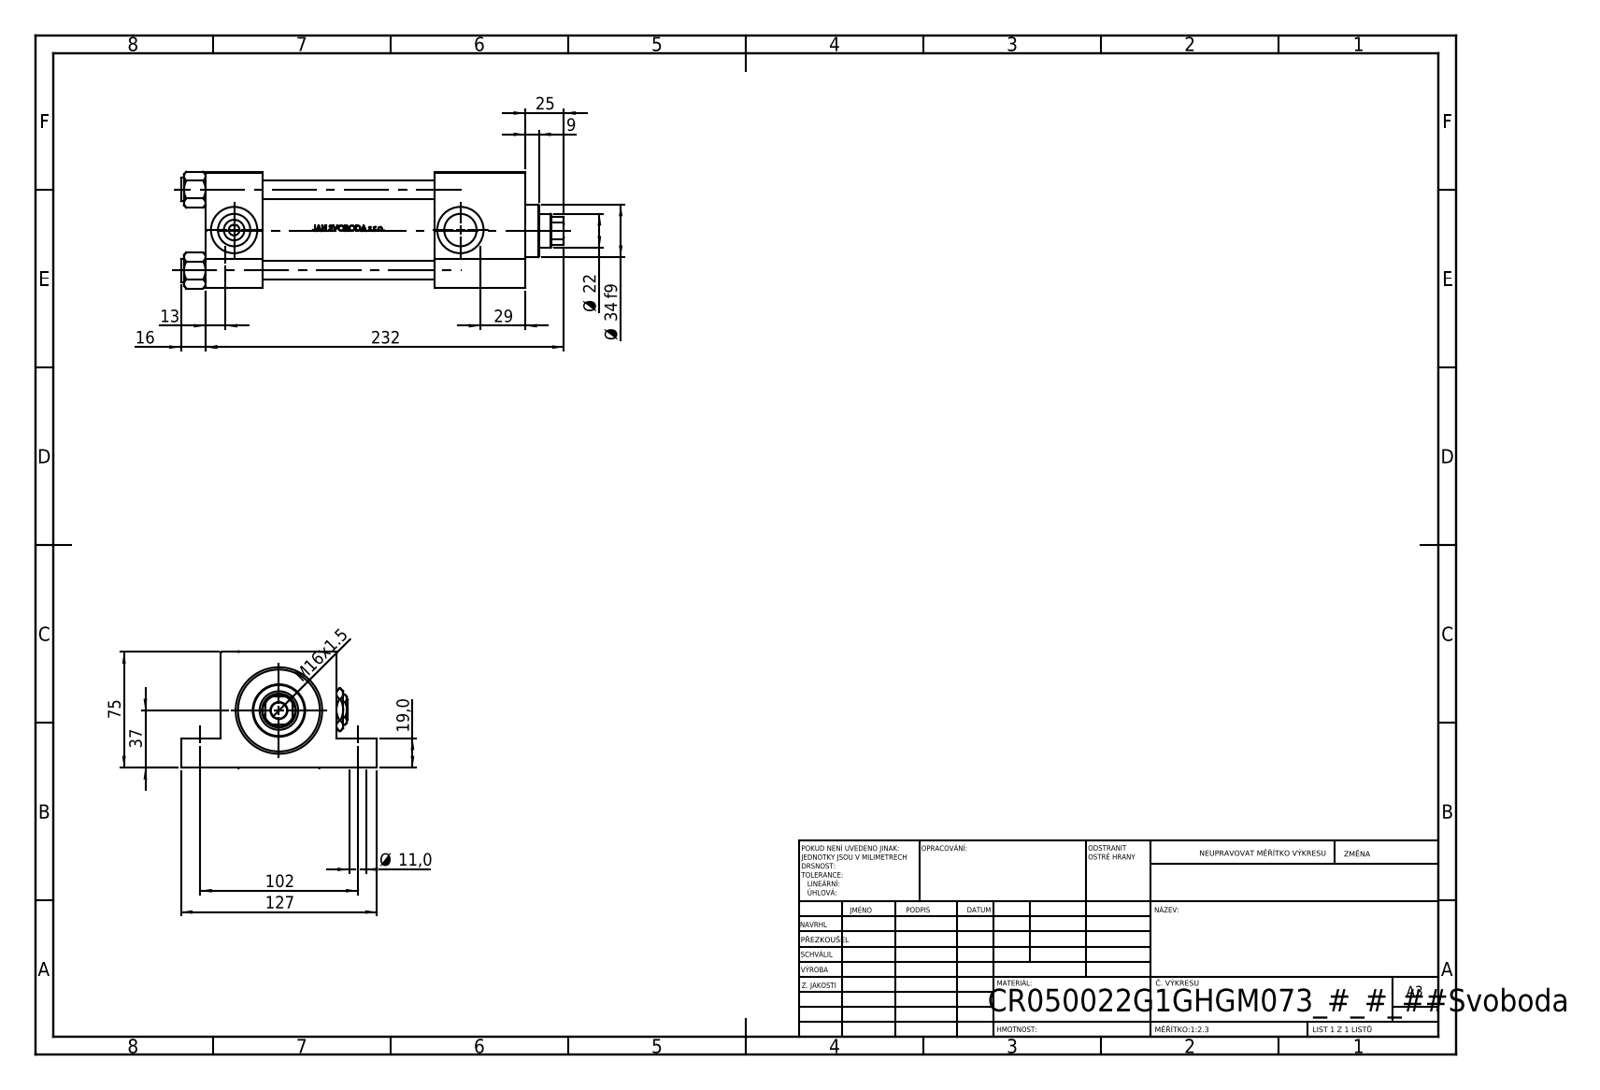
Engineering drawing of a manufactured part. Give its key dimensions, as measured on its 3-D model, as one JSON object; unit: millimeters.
{"part_name": "V215_VC_A; Zatka_pro_OIL_PORT; V215CR_G_Body; V215CR_VCP_G (+2 more)", "step_written_by": "SolidWorks 2019 (CONFIG_CONTROL_DESIGN)", "units": "millimeters", "bodies": {"solids": 12, "faces": 1134, "planar": 454, "cylindrical": 128, "other": 552}, "overall_size": [248, 127, 75.54], "volume_mm3": 823001, "surface_area_mm2": 190608, "round_holes": [[11, 4], [12, 4], [7, 2], [20.96, 2], [30, 2], [10.5, 1], [22, 1], [25, 1], [41, 1], [50, 1], [53, 1]], "round_bosses_or_shafts": [[15, 4], [56, 1], [34, 1]], "partial_cylinders_radius": [[10.5, 1]], "face_to_face_distances": [75, 37, 207, 170, 19, 56, 148, 111, 59, 26], "hole_center_spacings": [52.3, 36.63, 37.34, 73.96, 102, 165, 193.98, 146.5]}
